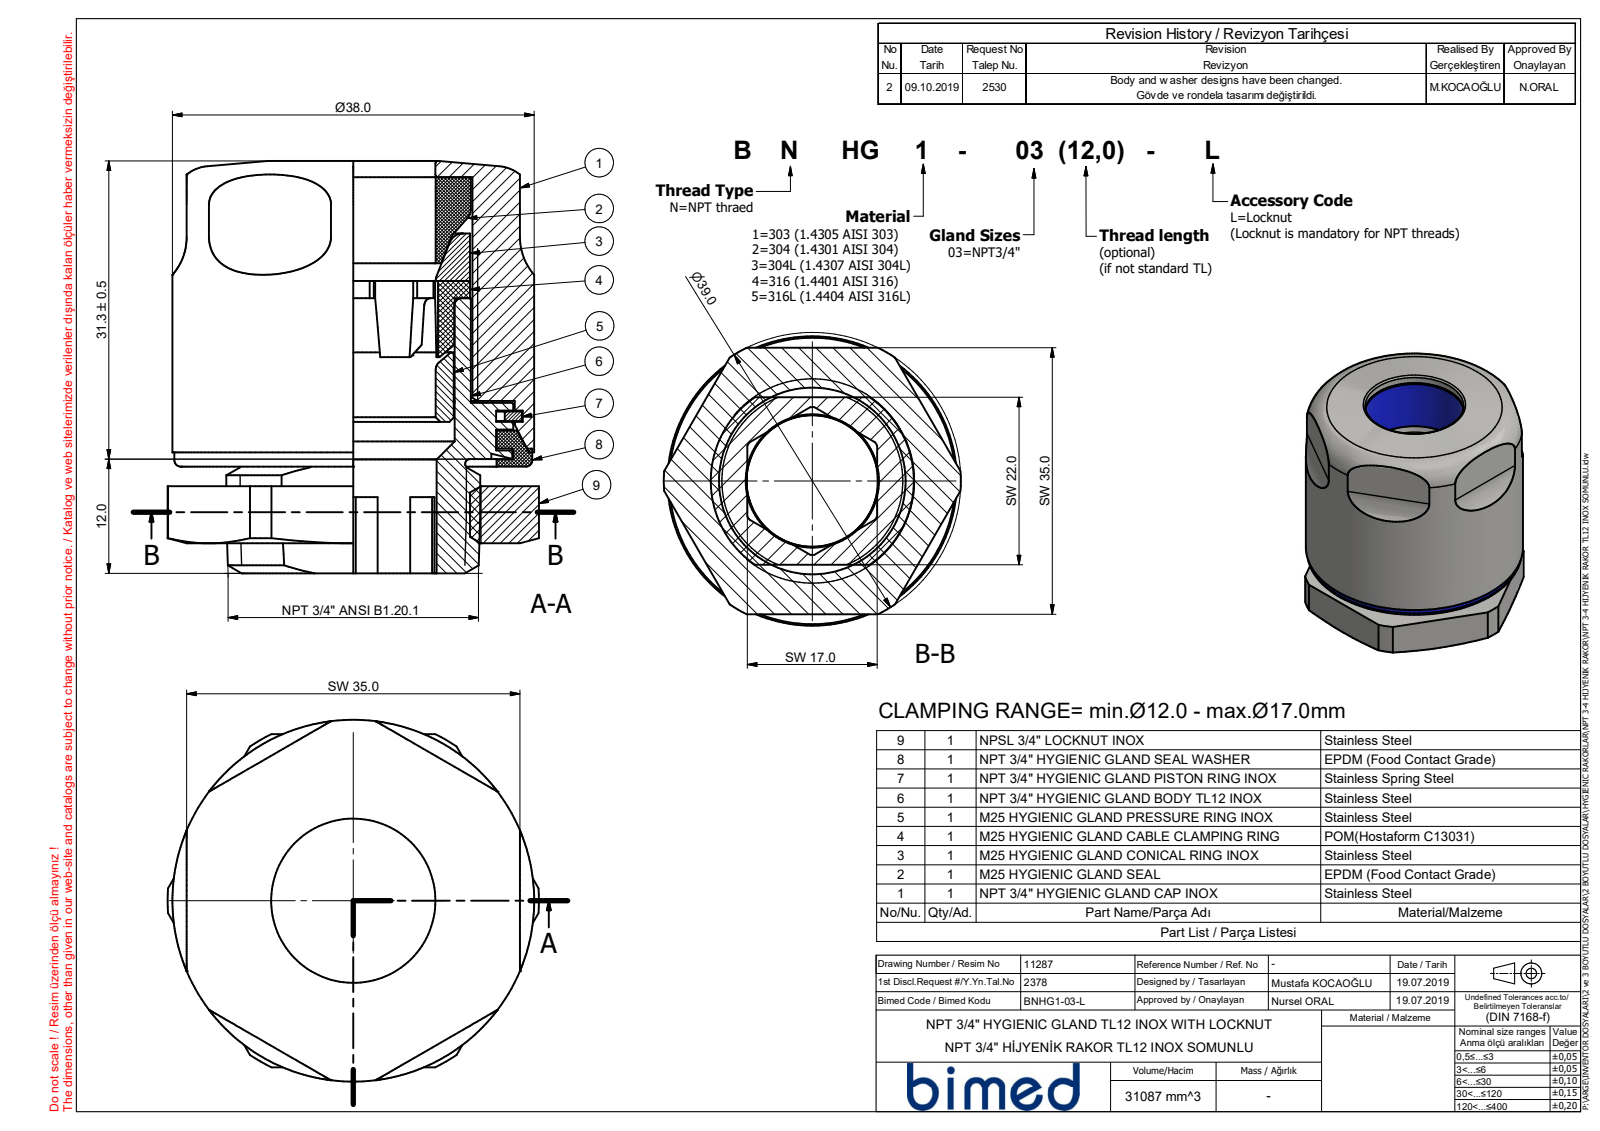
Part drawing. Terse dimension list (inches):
name: BNHG1-03-L
written by: SolidWorks 2021 (CONFIG_CONTROL_DESIGN)
unit: in
bodies: 1 solid, 57 faces (15 planar, 10 cylindrical, 32 other)
size: 1.736 × 1.535 × 1.496
volume: 2.719 in³; area: 12.51 in²
bosses: 1× ⌀1.496, 1× ⌀1.48
rounds: 1× R0.768
face distances: 0.081, 0.236, 0.317, 0.124, 0.36, 0.441, 1.378, 0.256, 1.122, 0.866
